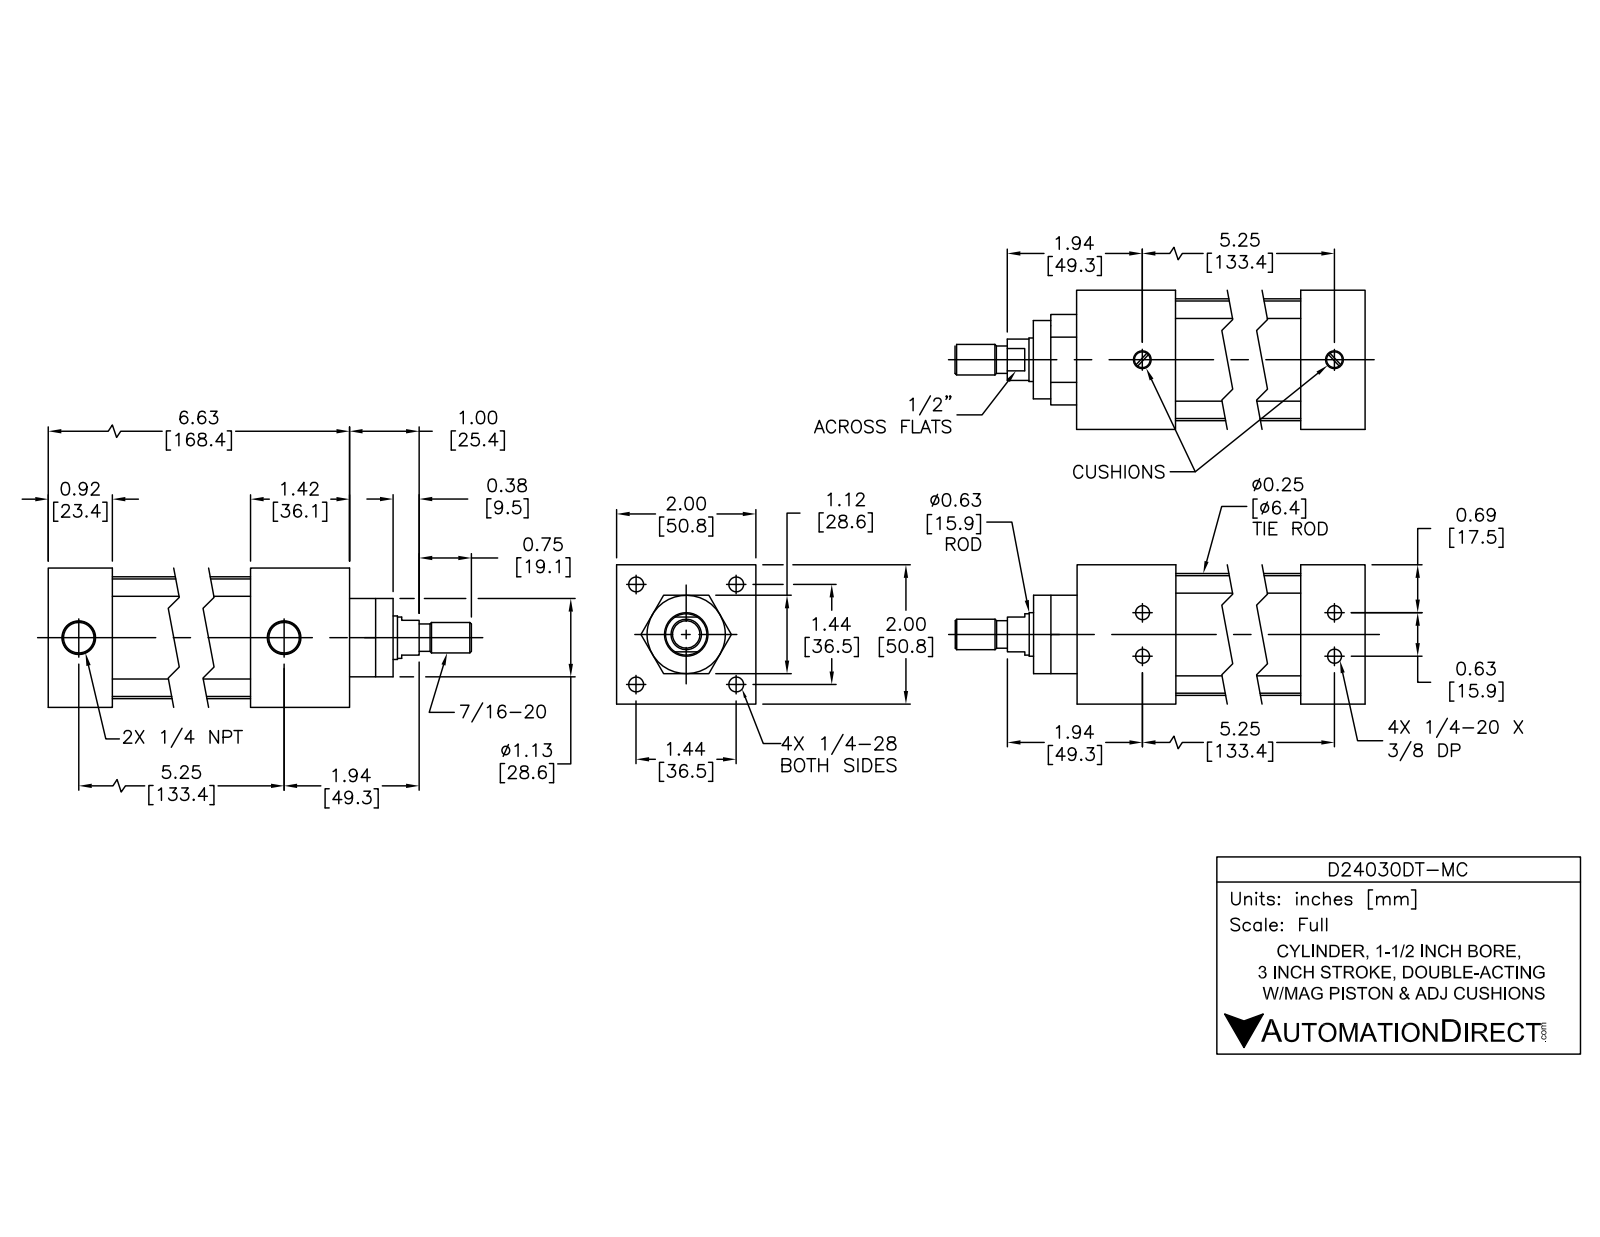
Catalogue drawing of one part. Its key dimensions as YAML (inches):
part_name: "D24030DT-MC; D24030DT-M BODY; D24030DT-M PISTON"
step_written_by: "SolidWorks 2015 (AUTOMOTIVE_DESIGN)"
units: inches
bodies: {solids: 12, faces: 303, planar: 99, cylindrical: 114, other: 90}
overall_size: [8.371, 2, 2]
volume: 15.98
surface_area: 137.9
round_holes:
  - {diameter: 0.196, count: 4}
  - {diameter: 0.211, count: 4}
  - {diameter: 0.281, count: 4}
  - {diameter: 0.406, count: 4}
  - {diameter: 0.297, count: 2}
  - {diameter: 0.477, count: 2}
  - {diameter: 0.625, count: 1}
  - {diameter: 0.628, count: 1}
  - {diameter: 1.5, count: 1}
round_bosses_or_shafts:
  - {diameter: 0.39, count: 4}
  - {diameter: 0.25, count: 4}
  - {diameter: 0.222, count: 4}
  - {diameter: 1.75, count: 1}
  - {diameter: 1.497, count: 1}
  - {diameter: 1.121, count: 1}
  - {diameter: 0.622, count: 1}
  - {diameter: 0.59, count: 1}
partial_cylinders:
  - {radius: 0.2, count: 4}
face_to_face_distances: [2, 6.621, 1.42, 5.201, 5.701, 4.281, 0.92, 1.121, 5.601, 4.181]
hole_center_spacings: [0.313, 1.014, 1.434, 0.625, 2.028, 5.247, 5.255, 5.256]
